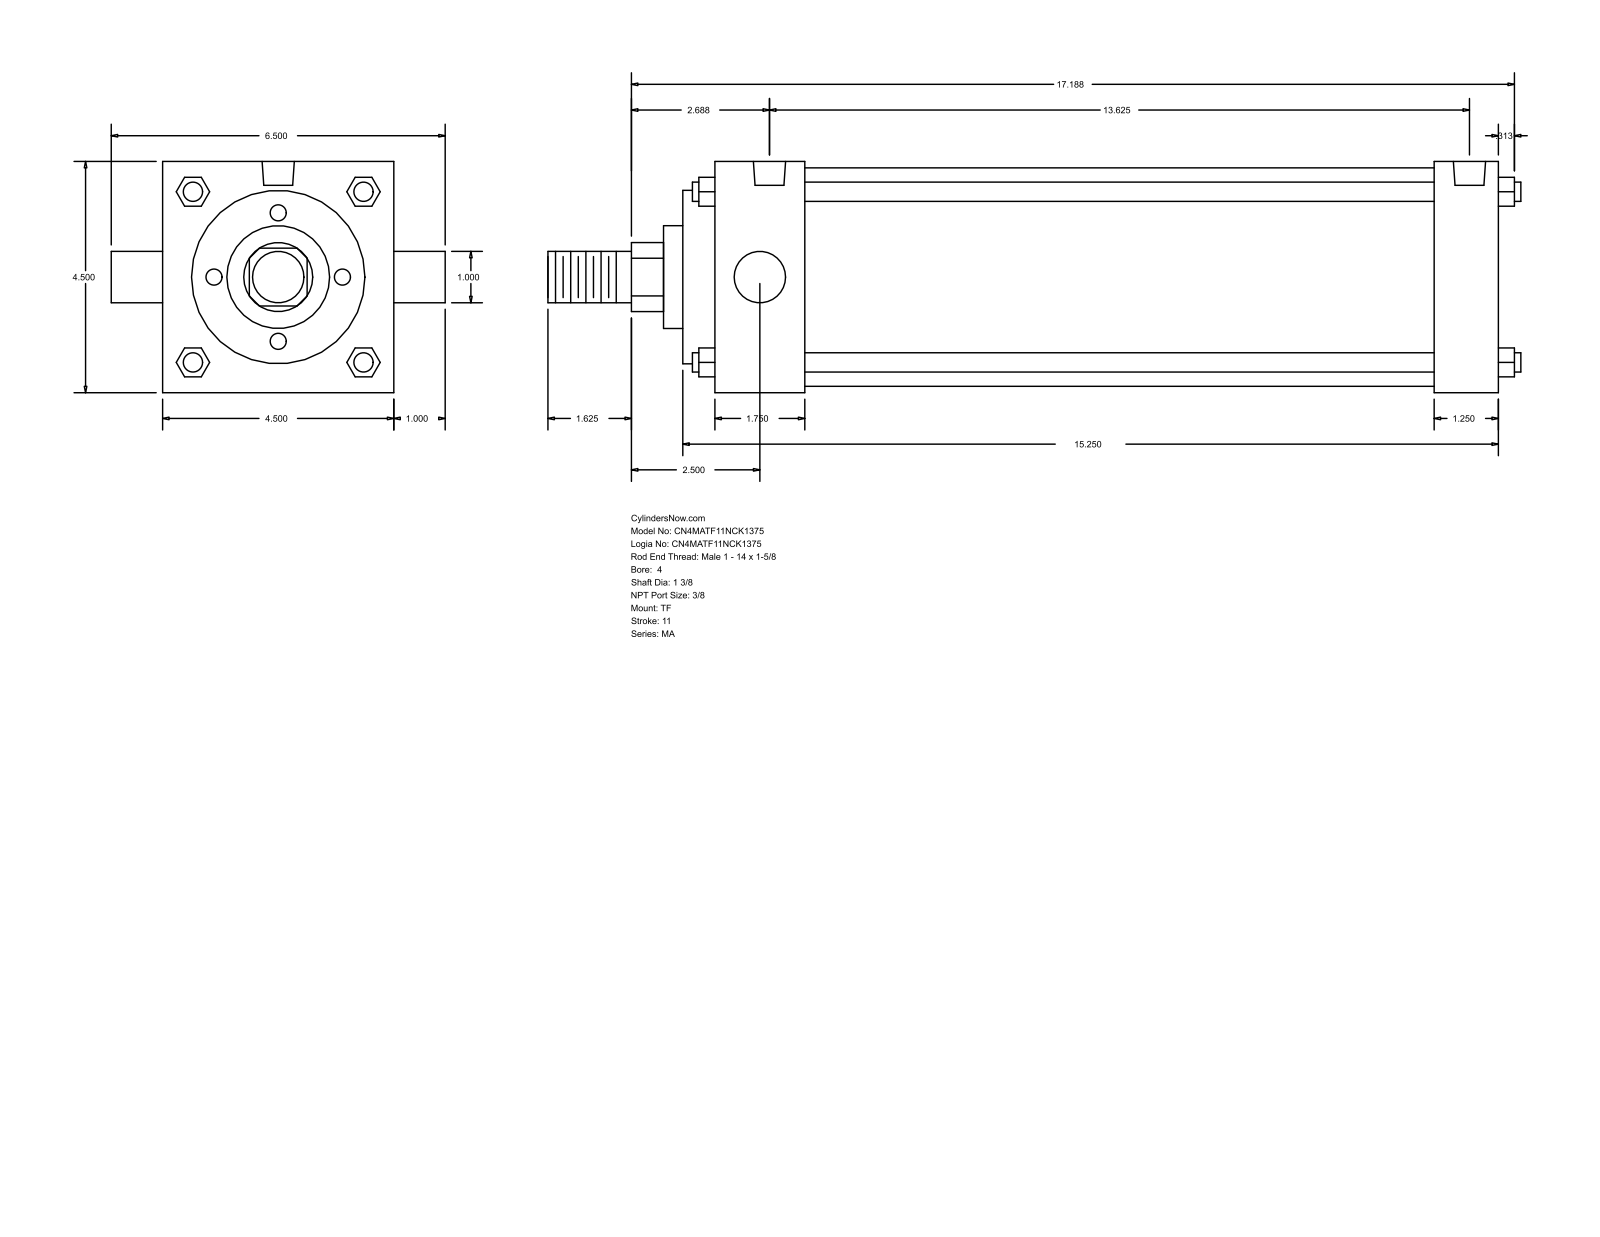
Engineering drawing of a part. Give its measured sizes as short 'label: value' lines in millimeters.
name: MA_TF__0400_1.375
written by: GSSL Pune (CONFIG_CONTROL_DESIGN)
unit: mm
bodies: 0 solids, 122 faces (93 planar, 29 cylindrical, 0 other)
size: 481.01 × 165.1 × 114.3
holes: 3× ⌀11.11, 2× ⌀15.93
bosses: 4× ⌀9.53, 2× ⌀25.4, 1× ⌀107.95, 1× ⌀85.72, 1× ⌀50.8, 1× ⌀34.92
rounds: 1× R17.06
face distances: 114.3, 387.35, 403.22, 15.87, 371.48, 355.61, 31.74, 60.32, 44.45, 311.16
hole spacings: 4.77, 341.31, 336.54, 346.08
